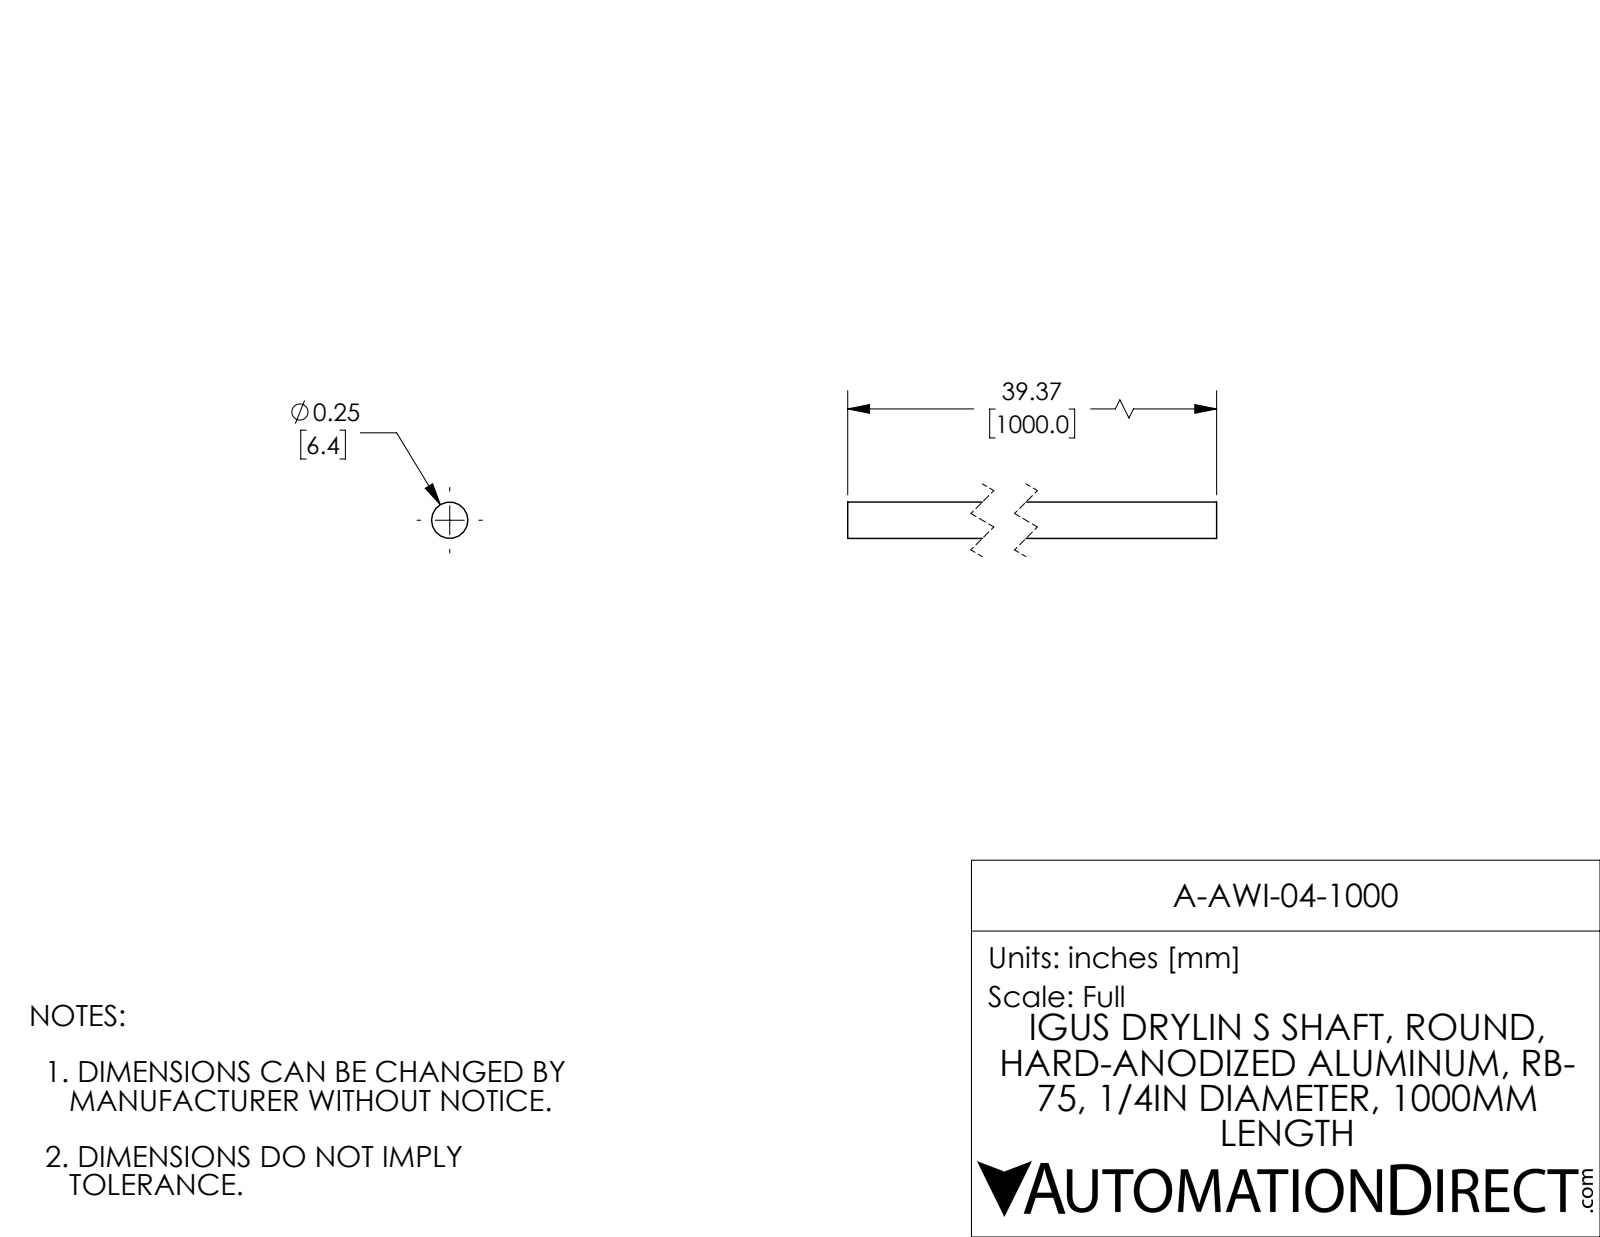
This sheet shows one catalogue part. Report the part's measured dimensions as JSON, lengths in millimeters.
{"part_name": "A-AWI-04-1000", "step_written_by": "SolidWorks 2017 (AUTOMOTIVE_DESIGN)", "units": "millimeters", "bodies": {"solids": 1, "faces": 4, "planar": 2, "cylindrical": 2, "other": 0}, "overall_size": [1000, 6.4, 6.4], "volume_mm3": 31680, "surface_area_mm2": 20010, "round_bosses_or_shafts": [[6.4, 1]], "face_to_face_distances": [1000]}
